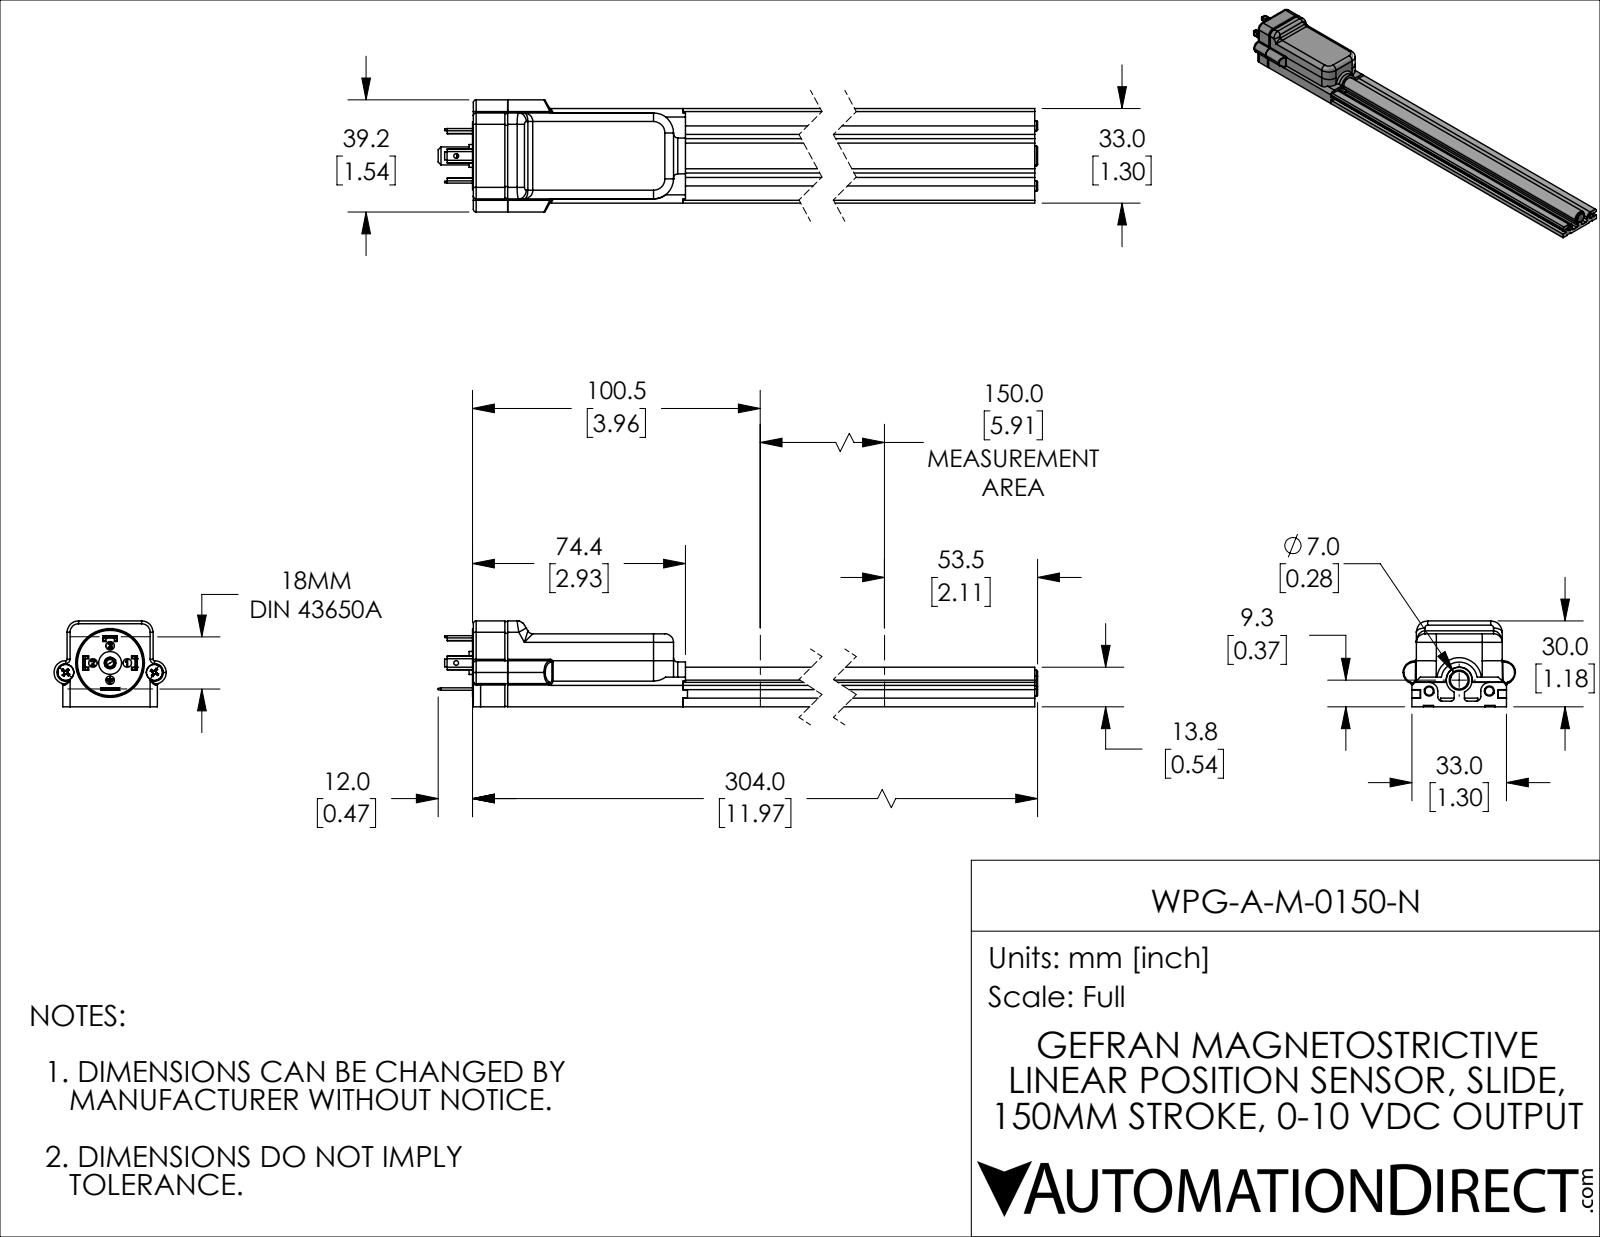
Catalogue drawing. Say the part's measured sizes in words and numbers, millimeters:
The part is named "WPG-A-M-0150-N". Its 3-D file was written by "SolidWorks 2021 (CONFIG_CONTROL_DESIGN)". It is 15 solids with 589 faces: 371 planar, 139 cylindrical and 79 other. Overall it measures 316 by 39.2 by 30 millimeters. Its volume is 113 345 cubic millimeters and its surface area 47 485 square millimeters. Round holes: 5 of diameter 3, 2 of diameter 1.5, 2 of diameter 1.65, 2 of diameter 3.2, 2 of diameter 5.7, 1 of diameter 1.6, 1 of diameter 2.5, 1 of diameter 4. Round bosses or shafts: 2 of diameter 5.6, 2 of diameter 3.5, 2 of diameter 2.85, 1 of diameter 9, 1 of diameter 8, 1 of diameter 7, 1 of diameter 5.3, 1 of diameter 3.94. Partial cylindrical surfaces (rounded edges, fillets, slot ends): 8 of radius 0.5, 8 of radius 3, 6 of radius 0.85, 5 of radius 1, 4 of radius 0.8, 4 of radius 1.5, 4 of radius 4.1, 4 of radius 7. The main face-to-face distances are 3, 1, 1.5, 2.5, 5.5, 6, 8.5, 22.5, 30, 0.5. The hole center spacings are 6, 8.49, 10.06, 12, 12.3, 15.73, 15.85, 18.08.
